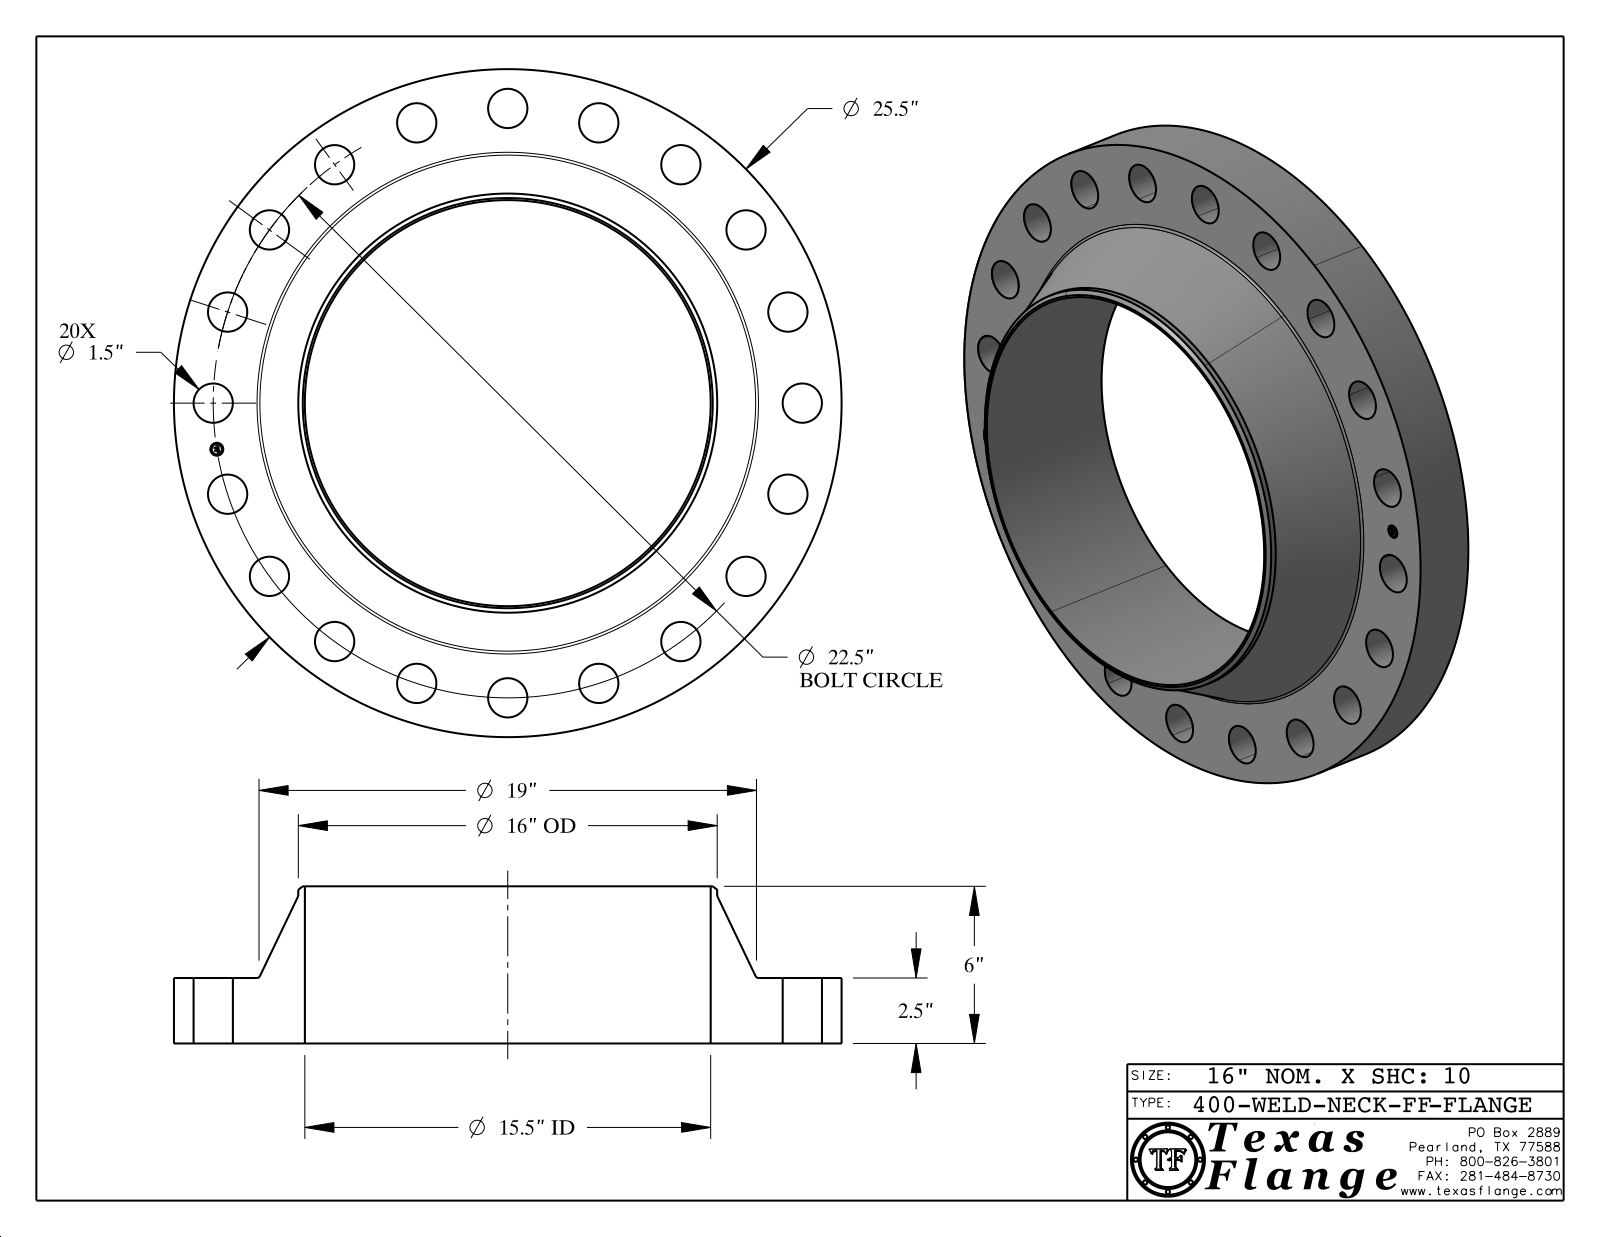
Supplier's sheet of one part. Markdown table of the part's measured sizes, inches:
| quantity | value |
| --- | --- |
| part name | 400-WELD-NECK-FF |
| STEP written by | CATIA V5 STEP AP214 (AUTOMOTIVE_DESIGN) |
| units | inches |
| bodies | 1 solid, 440 faces (368 planar, 66 cylindrical, 6 other) |
| overall size | 25.5 × 25.5 × 6 |
| volume | 884.9 in³ |
| surface area | 1 423 in² |
| round holes (diameter × count) | 1.5 × 20, 0.495 × 1, 15.5 × 1 |
| round bosses / shafts (diameter × count) | 0.03 × 8, 25.5 × 1, 16 × 1, 0.39 × 1 |
| main face-to-face distances | 2.5, 6, 3.5, 2.485, 0.015, 3.515, 0.148, 0.145, 0.027, 0.096 |
| hole center spacings | 11.25, 6.953, 13.225, 3.52, 18.203, 20.048, 21.399, 22.223 |
